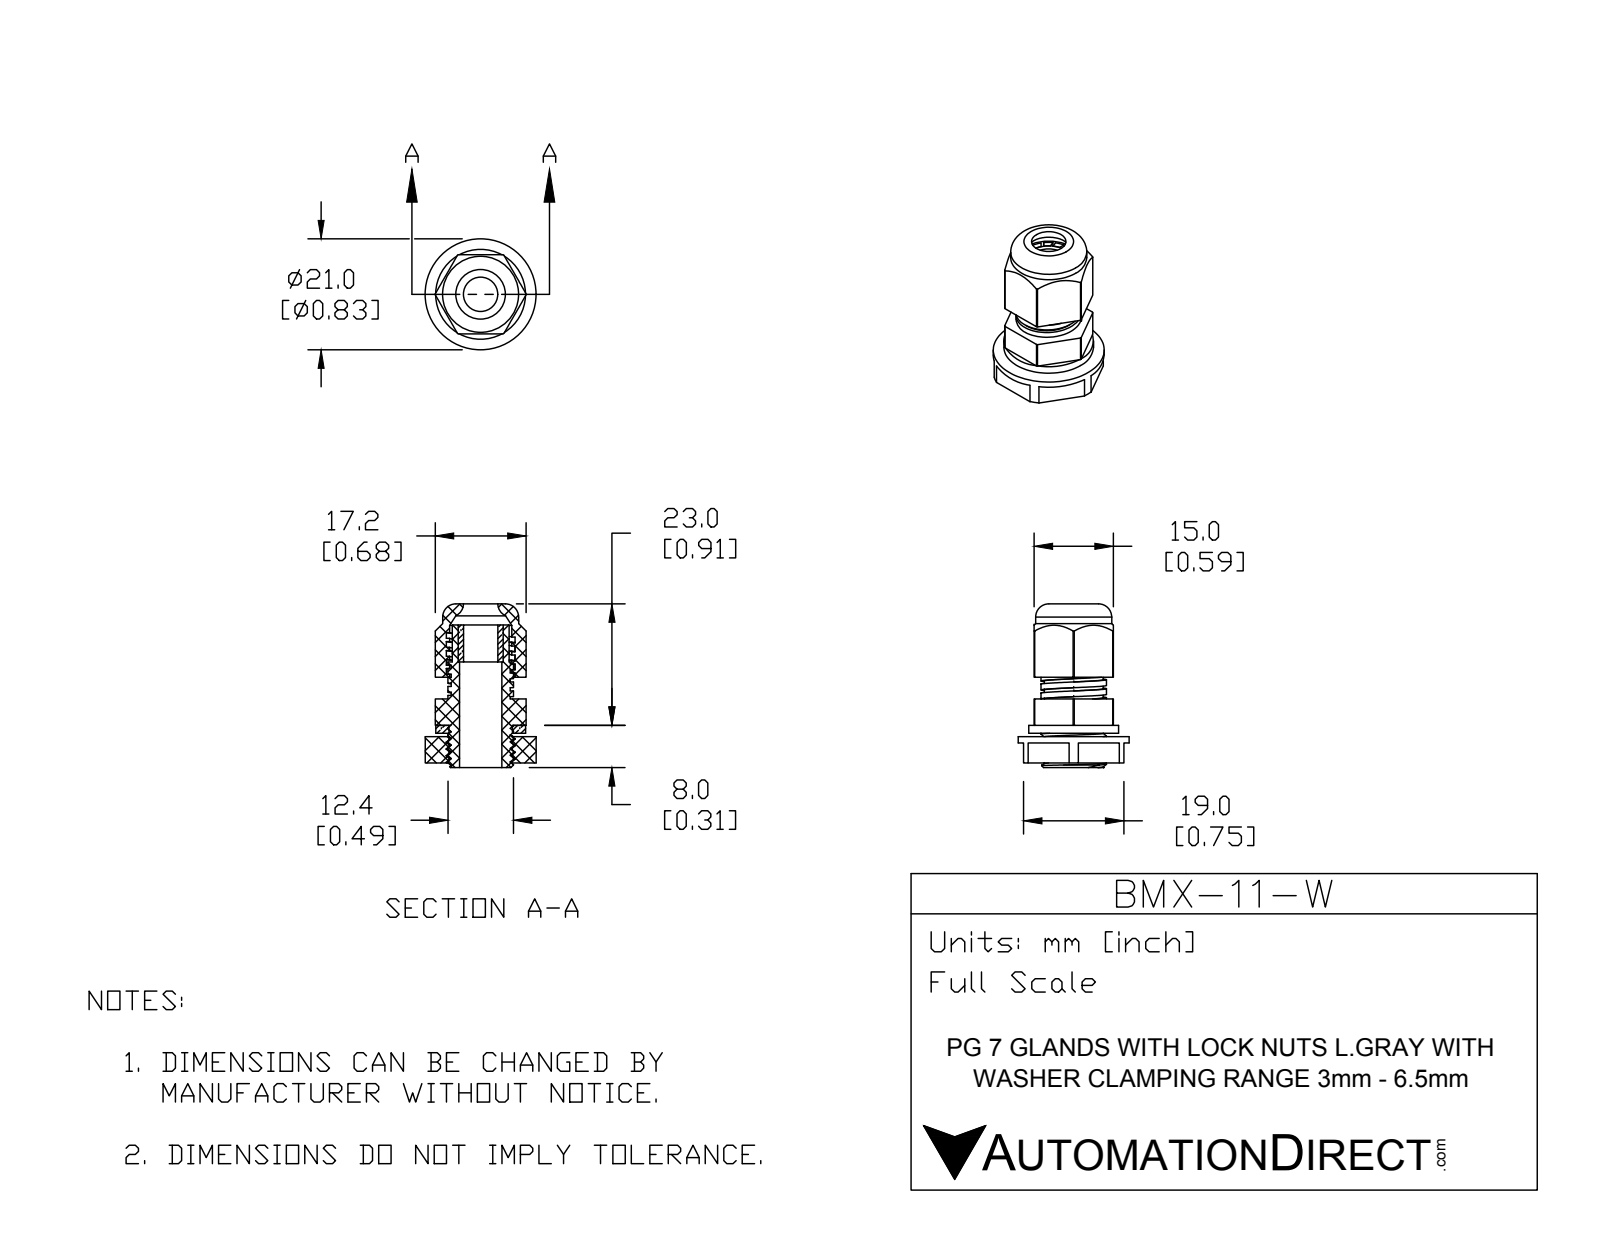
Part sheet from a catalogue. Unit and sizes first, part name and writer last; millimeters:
Units: millimetres
Overall size (bounding box): 31 × 21 × 21
Round holes (diameter × count): ⌀6.5 ×1, ⌀8 ×1, ⌀8.5 ×1, ⌀11.79 ×1, ⌀11.89 ×1, ⌀12 ×1
Round bosses / shafts (diameter × count): ⌀21 ×1, ⌀17 ×1, ⌀14.4 ×1, ⌀12.4 ×1, ⌀10.75 ×1
Partial cylindrical surfaces — rounded edges, fillets, slot ends (radius × count): R8.6 ×1
Main face-to-face distances: 15, 5, 7.12, 2, 17, 2.12, 19, 6.5, 5.62, 0.62
Volume: 4 230 mm³ · Surface area: 5 859 mm²
Bodies: 5 solids, 198 faces (100 planar, 76 cylindrical, 22 other)
Part name (STEP PRODUCT): BMX-11-W
STEP written by: SolidWorks 2015 (CONFIG_CONTROL_DESIGN)
